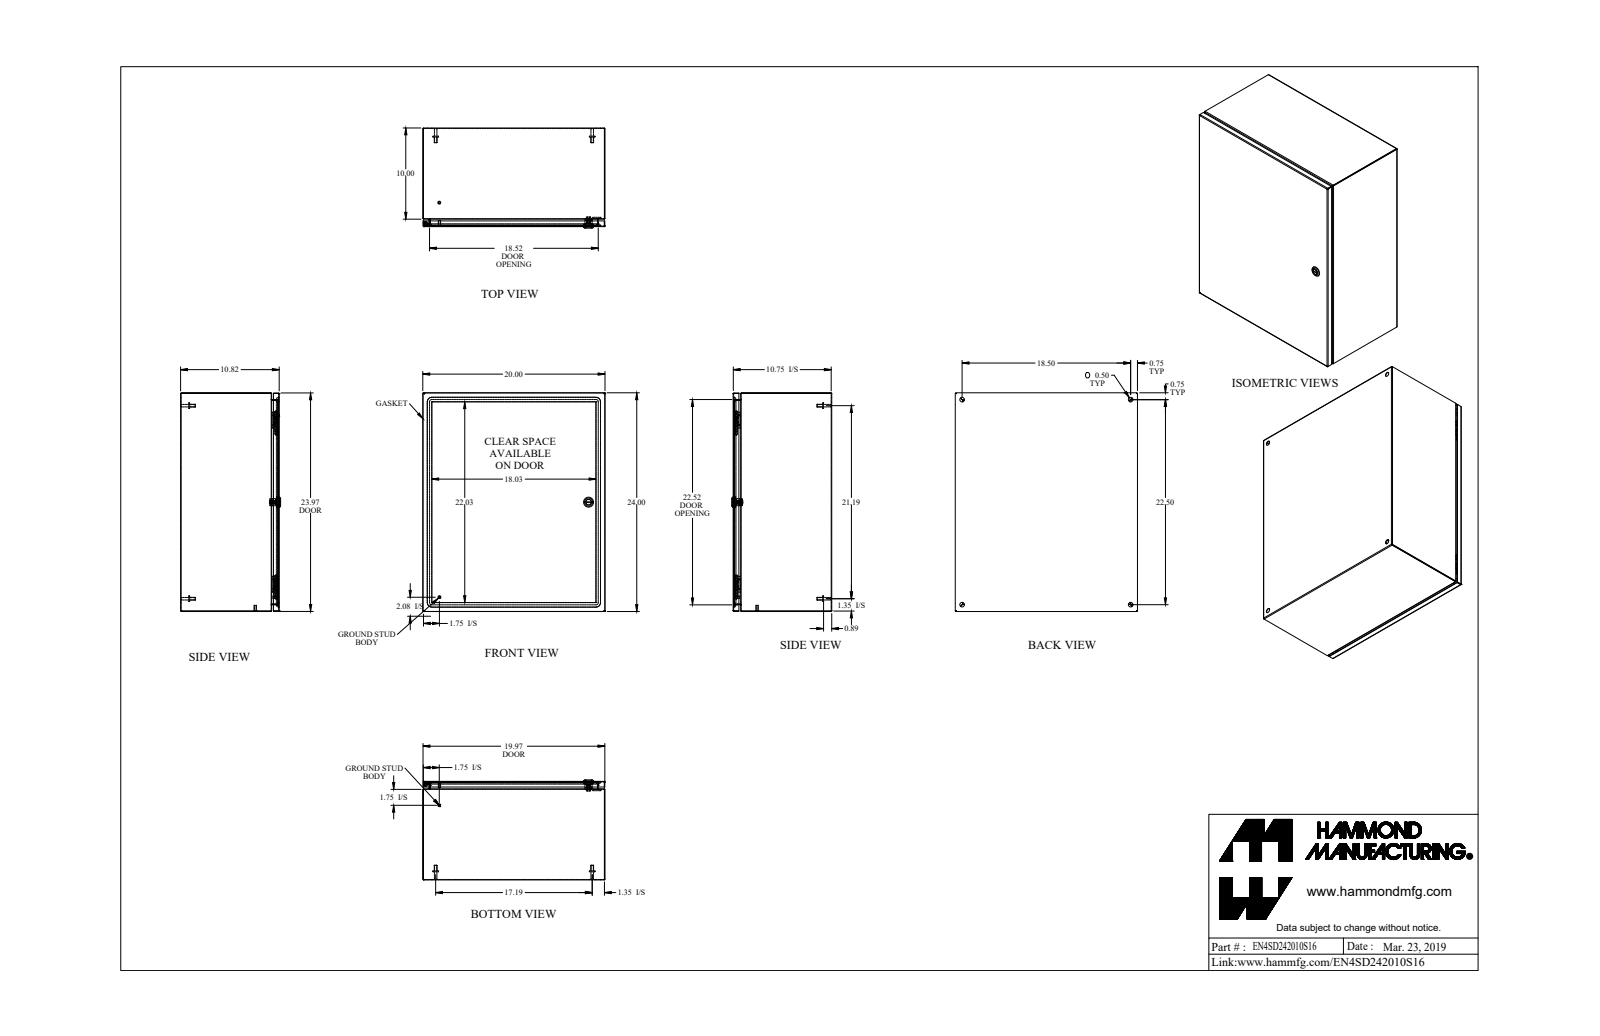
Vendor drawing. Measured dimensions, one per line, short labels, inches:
name: EN4SD242010S16_Default
written by: SolidWorks 2019 (CONFIG_CONTROL_DESIGN)
unit: in
bodies: 22 solids, 656 faces (303 planar, 211 cylindrical, 142 other)
size: 24 × 20 × 10.981
volume: 123.2 in³; area: 4 219 in²
holes: 5× ⌀0.5, 1× ⌀0.172, 1× ⌀0.197, 1× ⌀0.24, 1× ⌀0.242, 1× ⌀0.387, 1× ⌀0.63, 1× ⌀0.768
bosses: 6× ⌀0.313, 5× ⌀0.625, 4× ⌀0.275, 2× ⌀0.25, 1× ⌀1.1, 1× ⌀0.785, 1× ⌀0.525, 1× ⌀0.475
rounds: 21× R0.029, 21× R0.086, 12× R0.188, 4× R0.006, 4× R0.062, 4× R0.25, 4× R0.499, 2× R0.125
face distances: 0.057, 0.057, 10.707, 10.764, 10.764, 10.821, 19.943, 23.943, 19.886, 20
hole spacings: 11.3, 18.5, 20.754, 22.5, 29.129
